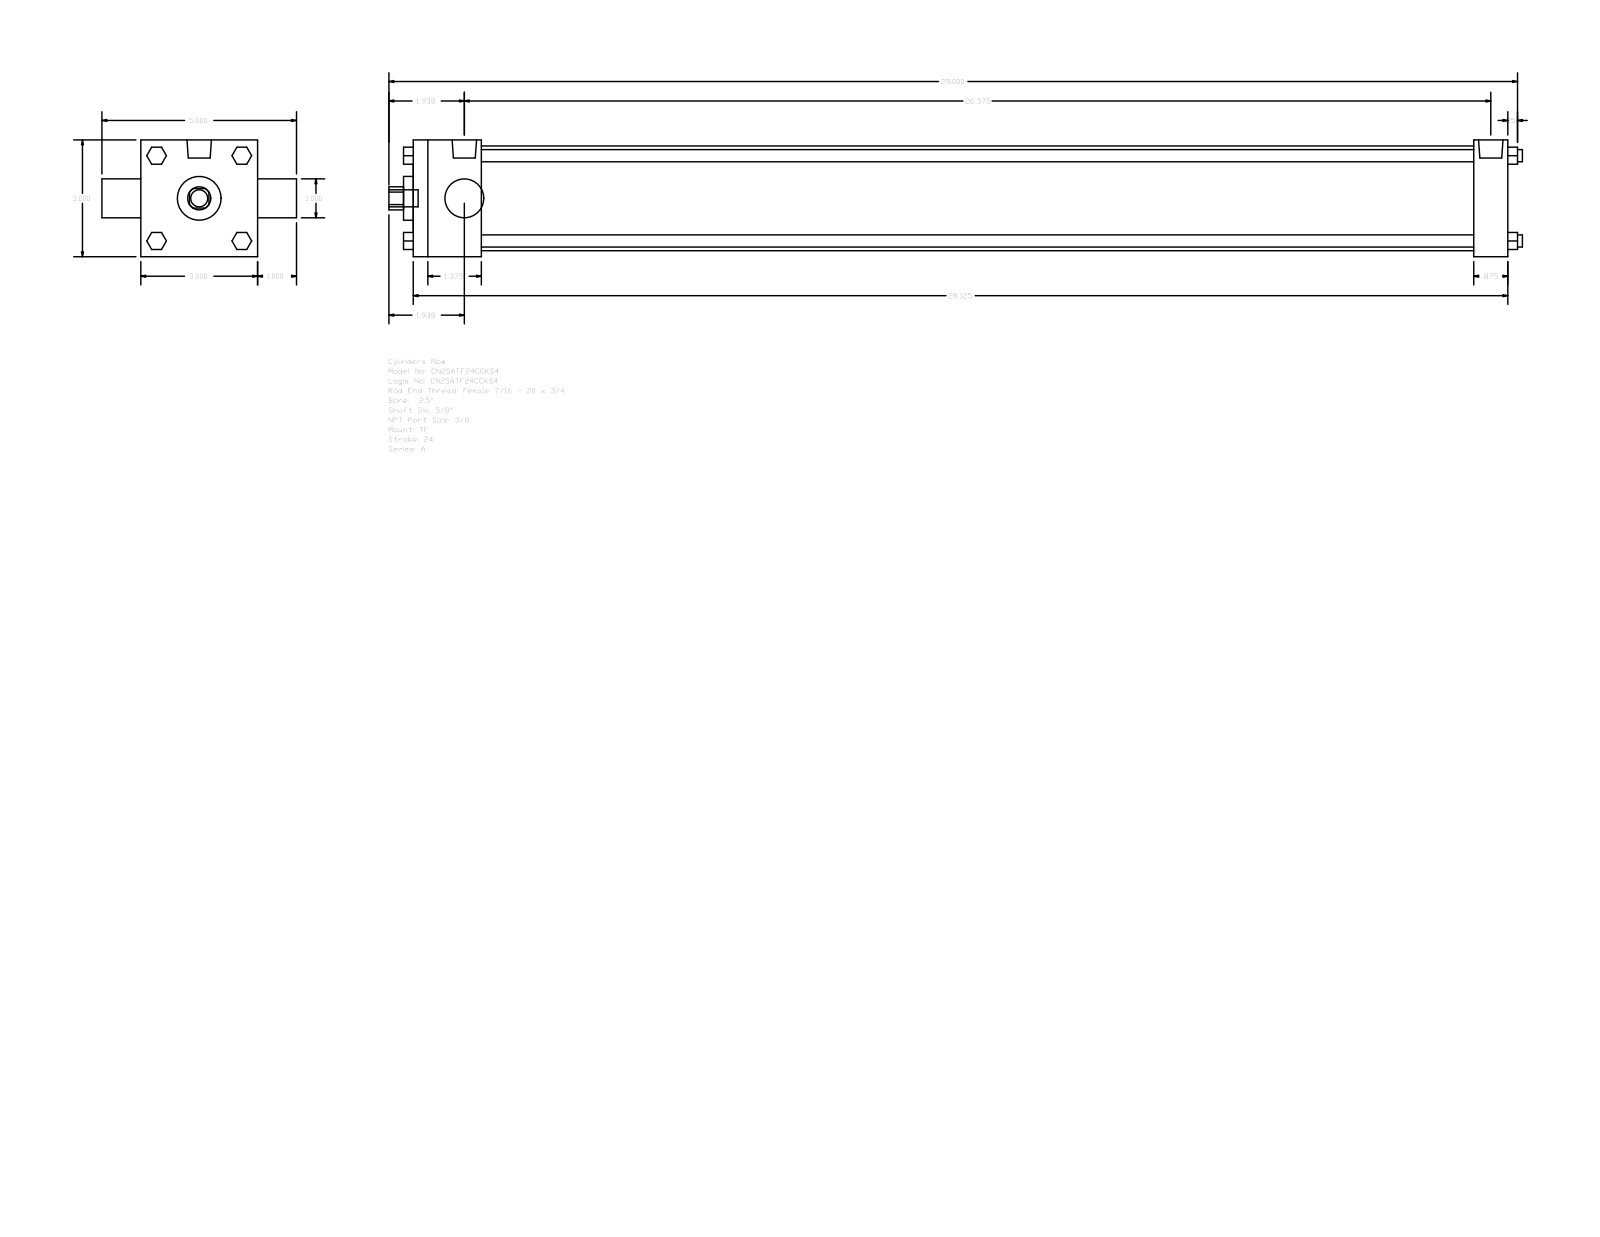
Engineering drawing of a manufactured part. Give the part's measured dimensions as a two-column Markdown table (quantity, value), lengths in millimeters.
| quantity | value |
| --- | --- |
| part name | A_TF__0250_0.625 |
| STEP written by | GSSL Pune (CONFIG_CONTROL_DESIGN) |
| units | millimeters |
| bodies | 0 solids, 120 faces (92 planar, 28 cylindrical, 0 other) |
| overall size | 739.77 × 127 × 76.2 |
| round holes (diameter × count) | 15.88 × 1, 25.4 × 1, 28.57 × 1, 68.33 × 1 |
| round bosses / shafts (diameter × count) | 7.94 × 4, 5.56 × 3, 15.93 × 2, 11.11 × 1 |
| partial cylindrical surfaces (radius × count) | 7.54 × 1 |
| main face-to-face distances | 76.2, 714.37, 44.45, 692.14, 647.69, 669.92, 22.23, 25.4, 101.6, 720.72 |
